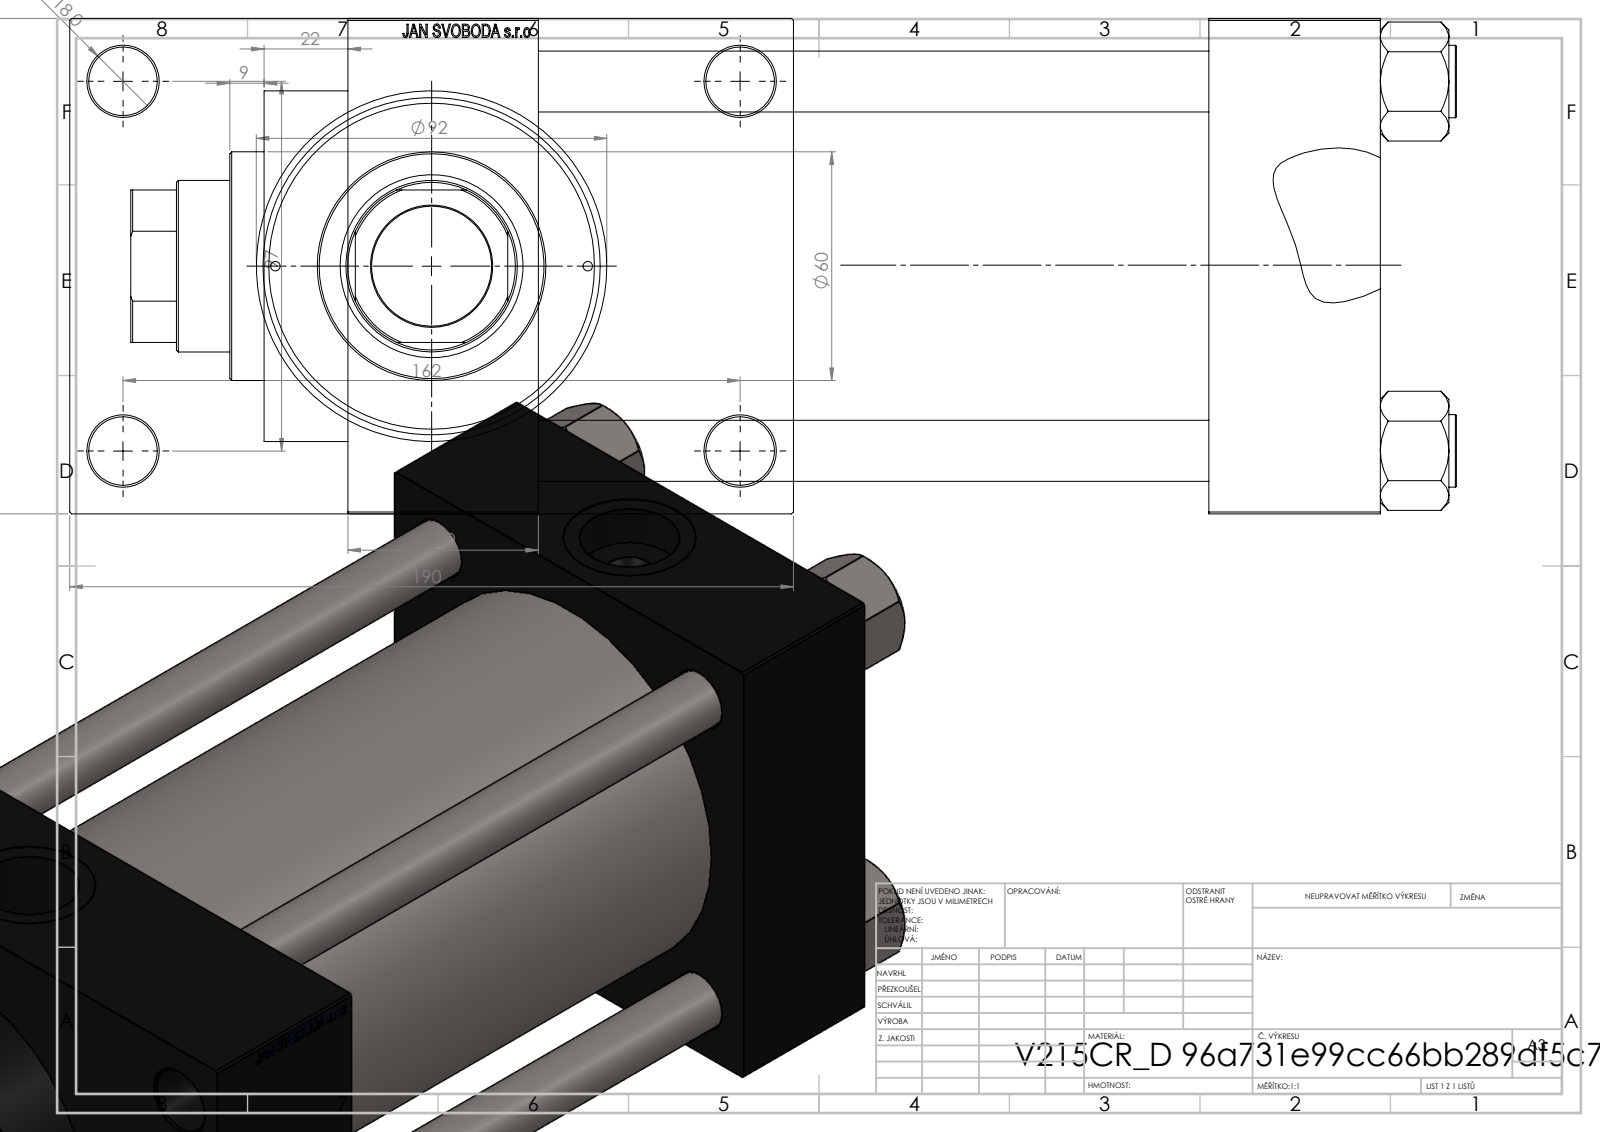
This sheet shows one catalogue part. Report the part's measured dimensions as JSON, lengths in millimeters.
{"part_name": "V215CR_D_TYCINKA; NUT_M5_D; V215CR_VCP_D; V215_VC_A (+1 more)", "step_written_by": "SolidWorks 2019 (CONFIG_CONTROL_DESIGN)", "units": "millimeters", "bodies": {"solids": 10, "faces": 1160, "planar": 547, "cylindrical": 93, "other": 520}, "overall_size": [348, 190, 130], "volume_mm3": 1148000, "surface_area_mm2": 456147, "round_holes": [[16, 4], [18, 4], [2.5, 2], [7, 2], [26.44, 2], [35, 2], [31.5, 1], [45, 1], [48, 1], [76, 1], [85.5, 1], [100, 1]], "round_bosses_or_shafts": [[19, 4], [106, 1], [92, 1], [60, 1]], "partial_cylinders_radius": [[22, 1]], "face_to_face_distances": [130, 45, 221, 176, 271, 226, 50, 30, 160, 190], "hole_center_spacings": [32.55, 49.02, 62.87, 68.52, 94.41, 96.9, 101.73, 102.27]}
